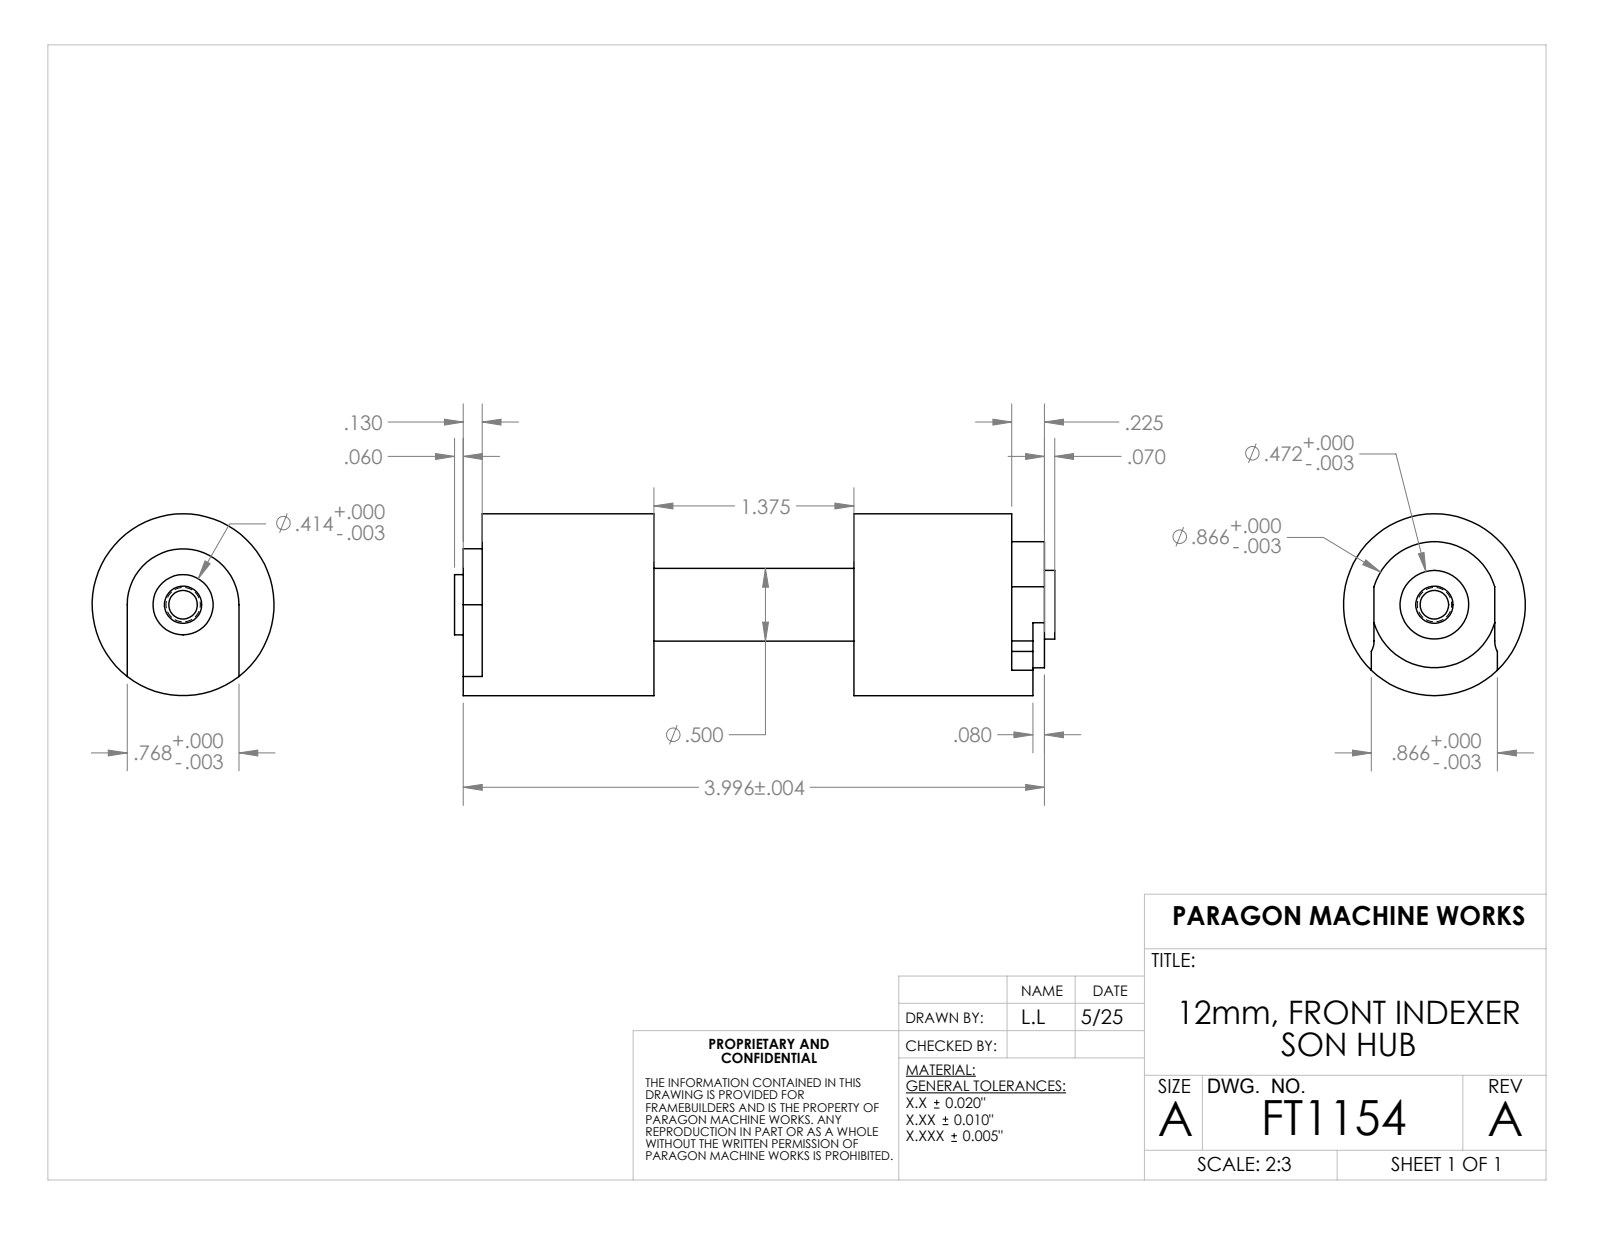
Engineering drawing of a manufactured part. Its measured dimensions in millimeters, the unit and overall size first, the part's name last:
Units: millimetres
Overall size (bounding box): 104.8 × 31.8 × 31.8
Round holes (diameter × count): ⌀5 ×1
Round bosses / shafts (diameter × count): ⌀31.8 ×1, ⌀22 ×1, ⌀12.7 ×1, ⌀12 ×1, ⌀10.5 ×1
Partial cylindrical surfaces — rounded edges, fillets, slot ends (radius × count): R3.8 ×2, R9.8 ×1
Main face-to-face distances: 34.9, 30, 64.9, 3.3, 33.3, 68.2, 95.8, 92.5, 62.5, 27.6
Volume: 53 500 mm³ · Surface area: 11 520 mm²
Bodies: 1 solid, 43 faces (15 planar, 20 cylindrical, 8 other)
Part name (STEP PRODUCT): FT1154
STEP written by: SolidWorks 2023 (AUTOMOTIVE_DESIGN)
